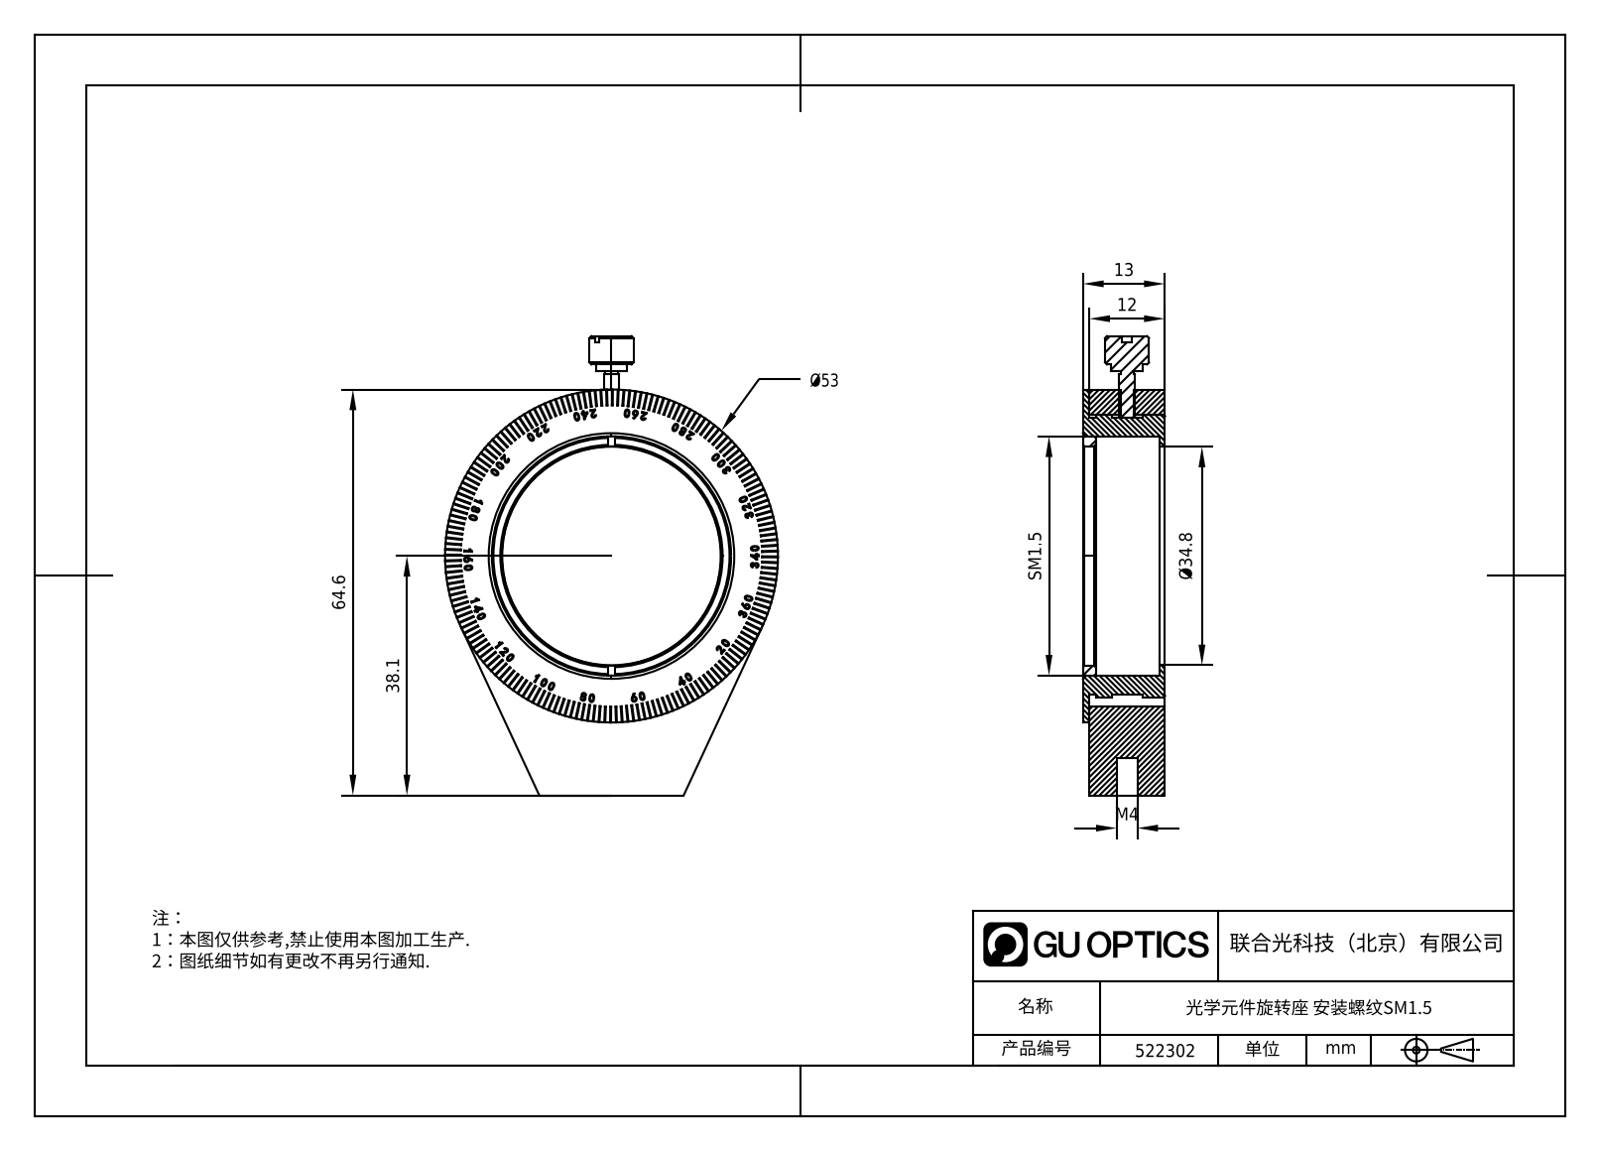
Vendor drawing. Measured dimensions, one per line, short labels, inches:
written by: SolidWorks 2021 (CONFIG_CONTROL_DESIGN)
unit: in
bodies: 4 solids, 1216 faces (986 planar, 35 cylindrical, 195 other)
size: 2.878 × 2.087 × 0.514
volume: 1.149 in³; area: 20.7 in²
holes: 1× ⌀0.081, 1× ⌀0.13, 1× ⌀1.37, 1× ⌀1.374, 1× ⌀1.5
bosses: 1× ⌀2.087, 1× ⌀1.772, 1× ⌀1.732, 1× ⌀0.276, 1× ⌀0.197, 1× ⌀0.098, 1× ⌀0.083
rounds: 1× R0.748
face distances: 0.039, 0.472, 0.512, 0.474, 0.514, 0.433, 0.031, 0.03, 0.443, 0.482
